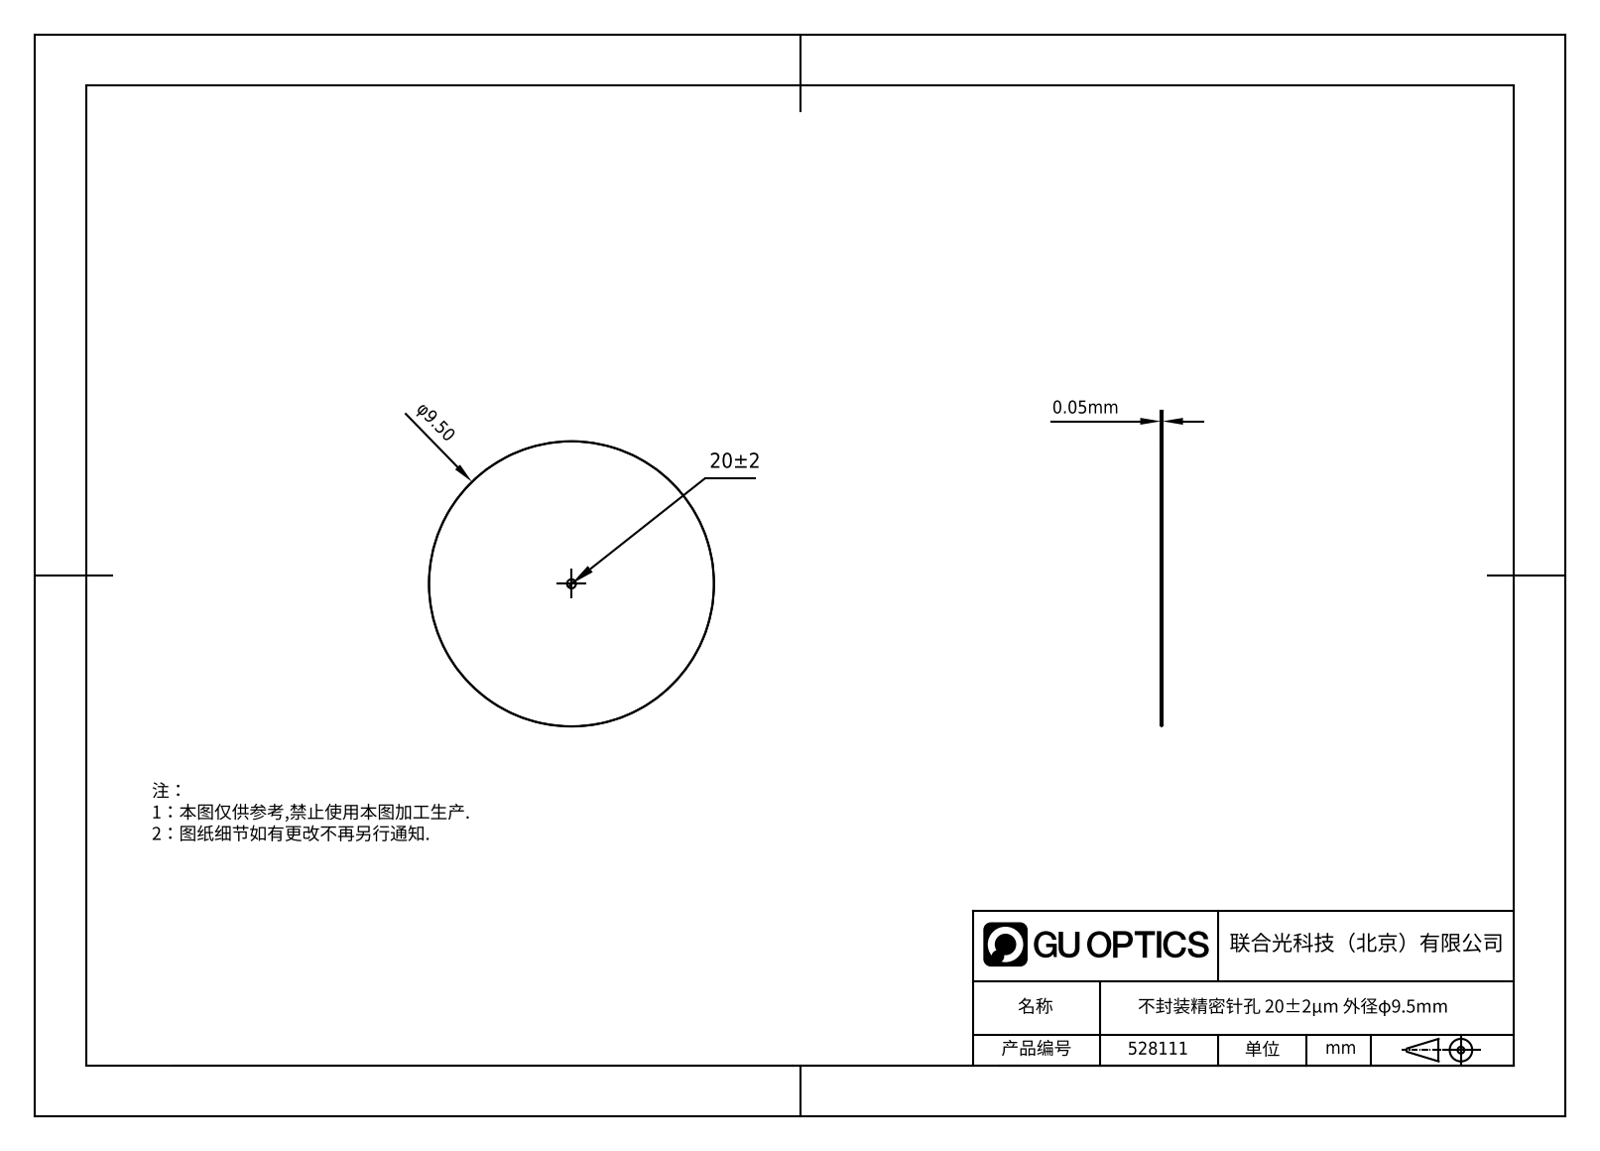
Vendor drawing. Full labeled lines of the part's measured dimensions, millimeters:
Part name (STEP PRODUCT): 1.5.3.4-ZXO-9.5-20
STEP written by: SolidWorks 2021 (CONFIG_CONTROL_DESIGN)
Units: millimetres
Bodies: 1 solid, 6 faces (2 planar, 4 cylindrical, 0 other)
Overall size (bounding box): 9.5 × 9.5 × 0.05
Volume: 4 mm³ · Surface area: 143 mm²
Round bosses / shafts (diameter × count): ⌀9.5 ×1
